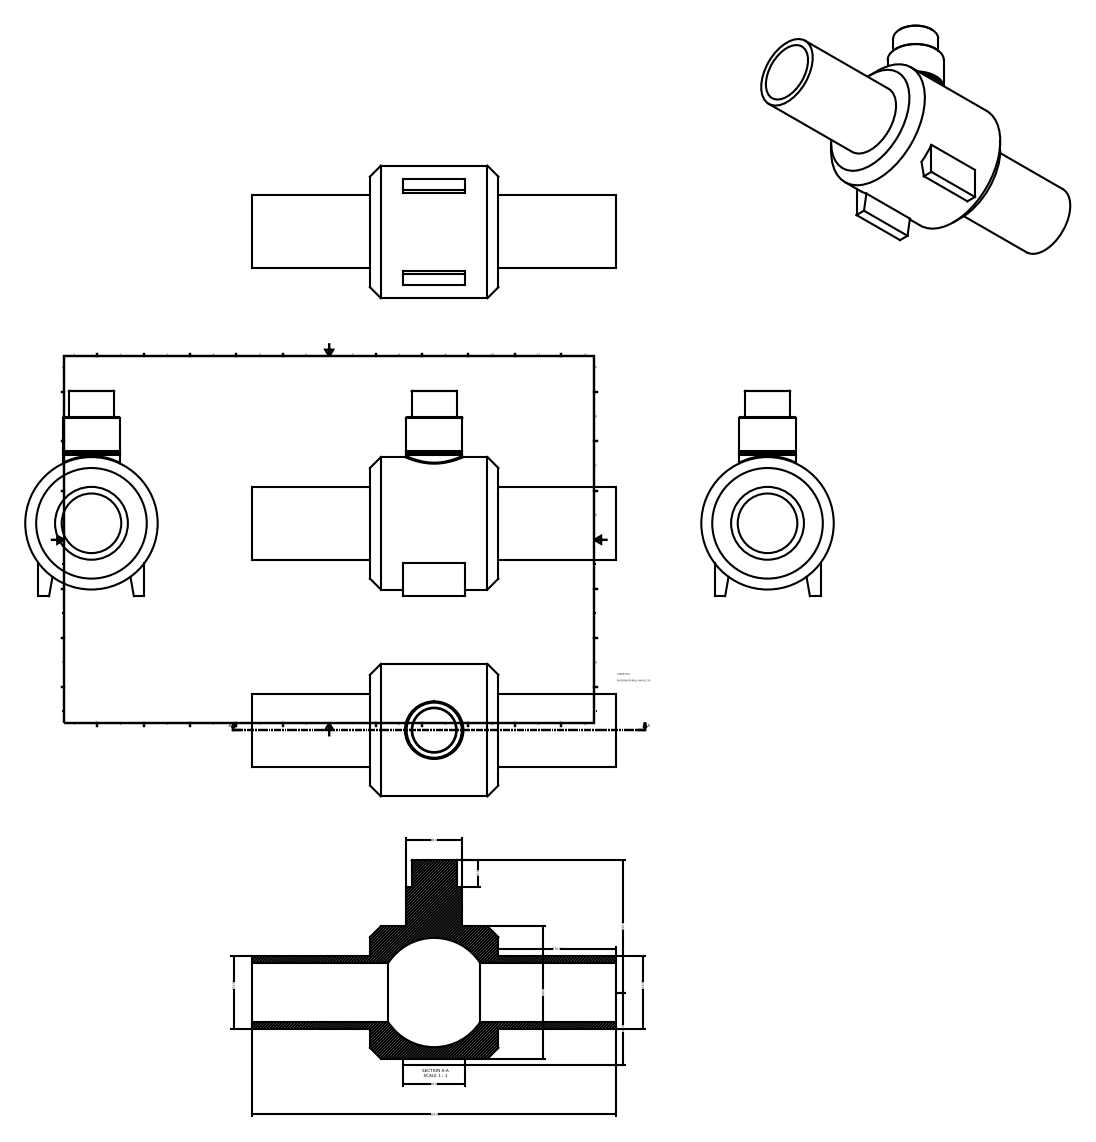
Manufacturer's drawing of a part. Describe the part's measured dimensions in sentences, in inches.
The part is named "436207110". Its 3-D file was written by "Autodesk Inventor 2015 (AUTOMOTIVE_DESIGN)". It is 1 solid with 33 faces: 16 planar, 9 cylindrical and 8 other. Overall it measures 21.654 by 12.205 by 7.874 inches. Its volume is 309.3 cubic inches and its surface area 792.5 square inches. Round holes: 1 of diameter 3.543. Round bosses or shafts: 1 of diameter 7.874, 1 of diameter 4.331, 1 of diameter 3.346, 1 of diameter 2.677. The main face-to-face distances are 7.638, 7.008, 14.646, 6.299, 21.654, 12.205, 8.996, 12.657, 1.988, 5.65.
